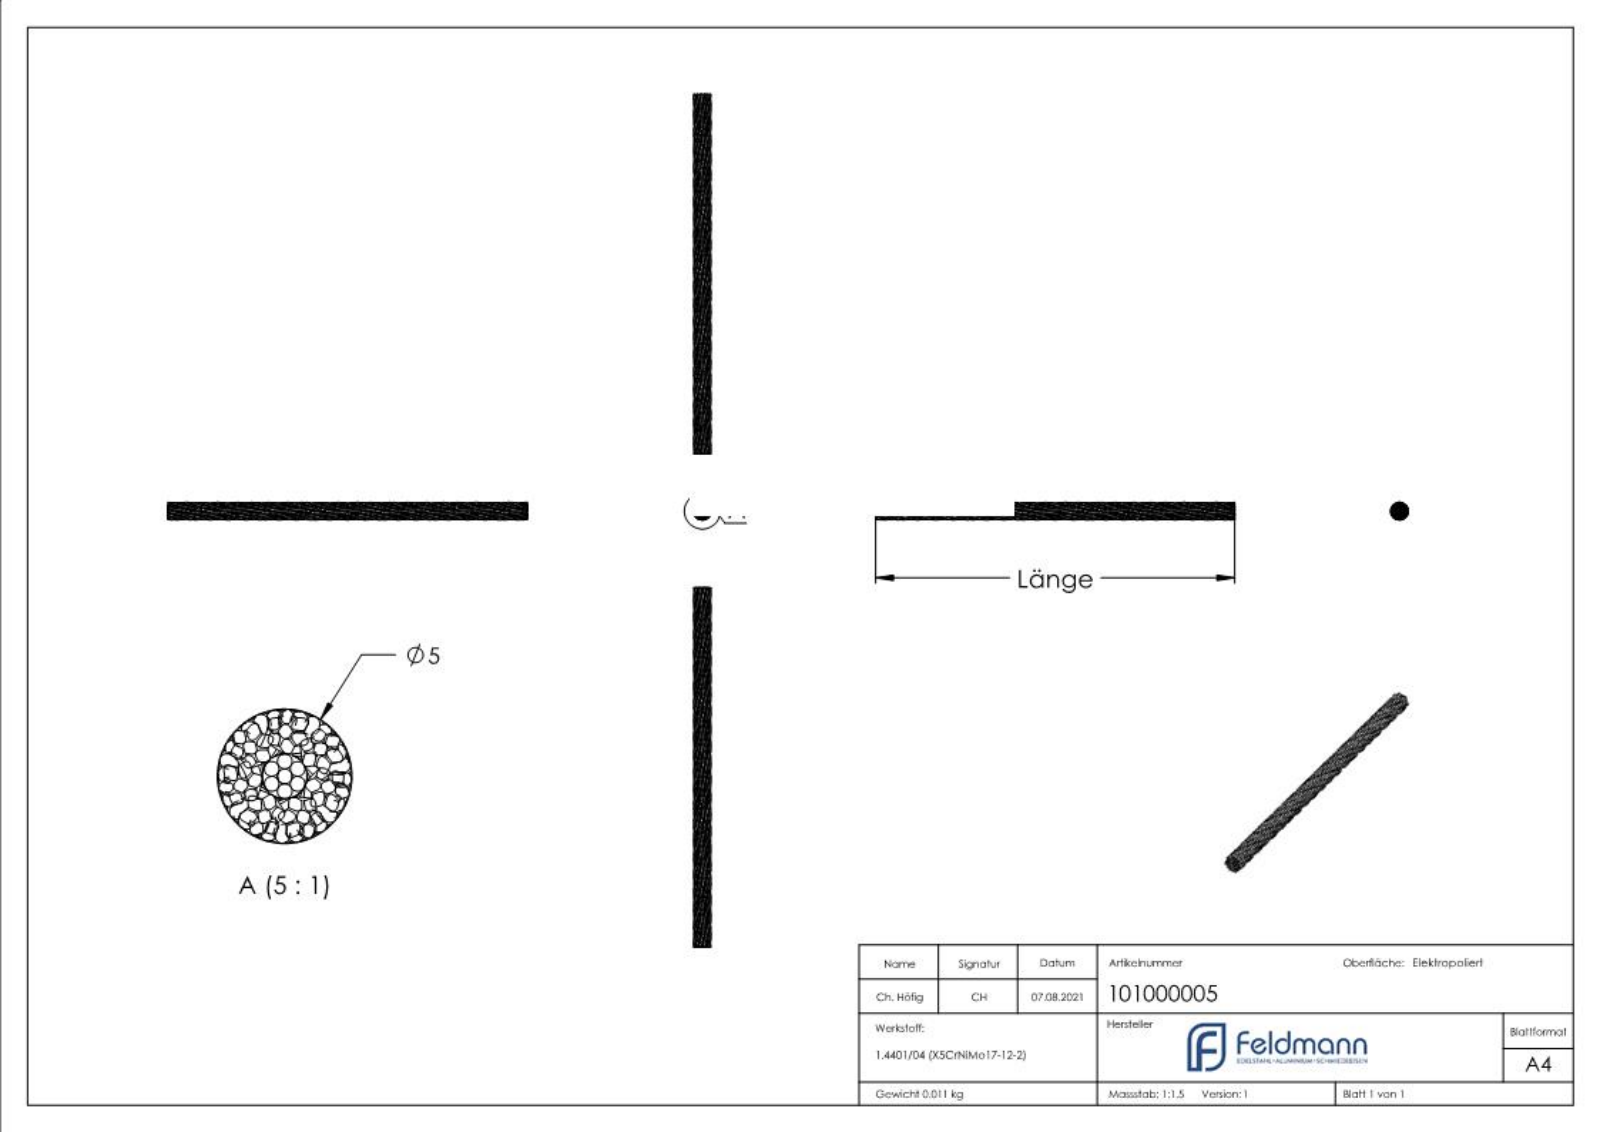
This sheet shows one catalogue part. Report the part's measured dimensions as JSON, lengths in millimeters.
{"part_name": "101000005", "step_written_by": "SolidWorks 2018 (CONFIG_CONTROL_DESIGN)", "units": "millimeters", "bodies": {"solids": 58, "faces": 223, "planar": 116, "cylindrical": 3, "other": 104}, "overall_size": [101, 6, 6], "volume_mm3": 1523, "surface_area_mm2": 10579, "round_bosses_or_shafts": [[6, 1], [1.1, 1], [0.56, 1]], "face_to_face_distances": [1, 100, 101]}
